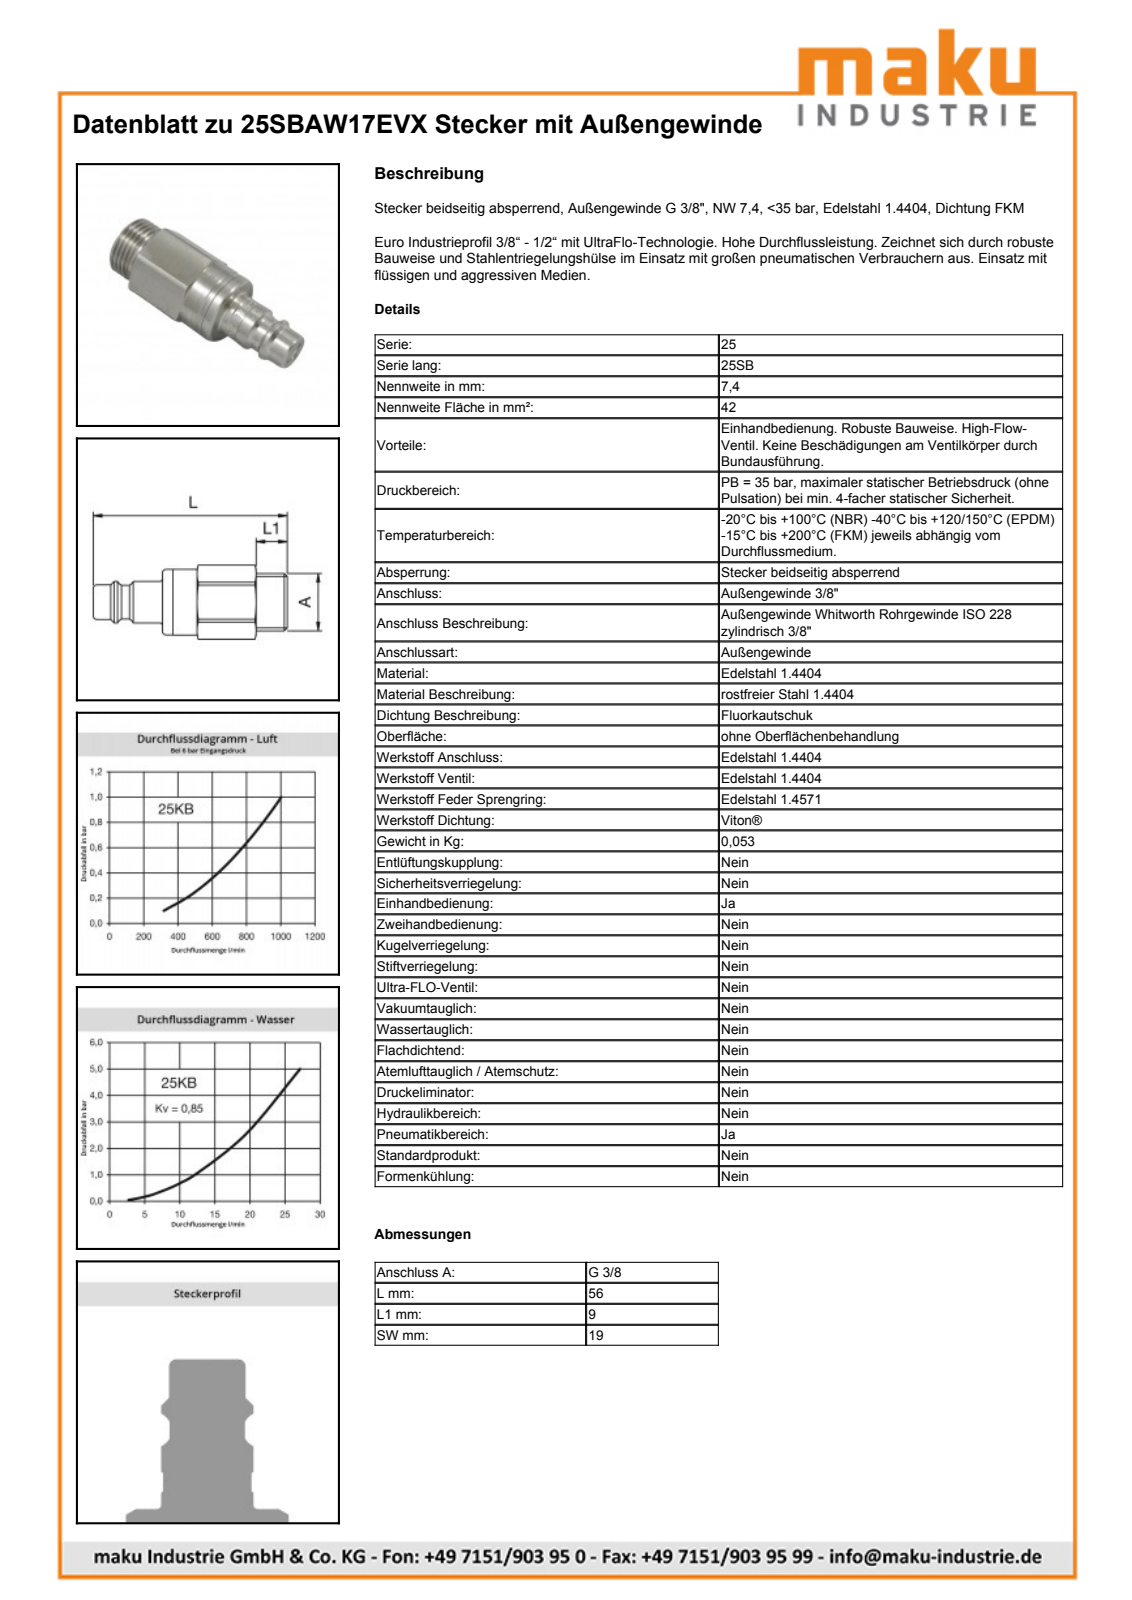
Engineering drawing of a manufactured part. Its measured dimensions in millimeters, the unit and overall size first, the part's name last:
Units: millimetres
Overall size (bounding box): 56 × 21.15 × 20.56
Round holes (diameter × count): ⌀15.1 ×1, ⌀16 ×1
Round bosses / shafts (diameter × count): ⌀19 ×1, ⌀18.95 ×1, ⌀16.66 ×1, ⌀14.83 ×1, ⌀14.5 ×1, ⌀12 ×1, ⌀9.9 ×1, ⌀9.75 ×1
Partial cylindrical surfaces — rounded edges, fillets, slot ends (radius × count): R10.7 ×1
Main face-to-face distances: 19, 36, 20, 56, 47, 27, 9, 3, 4.5, 23
Volume: 11 739 mm³ · Surface area: 4 223 mm²
Bodies: 1 solid, 54 faces (15 planar, 18 cylindrical, 21 other)
Part name (STEP PRODUCT): D110821
STEP written by: Autodesk Inventor 2013 (AUTOMOTIVE_DESIGN)
